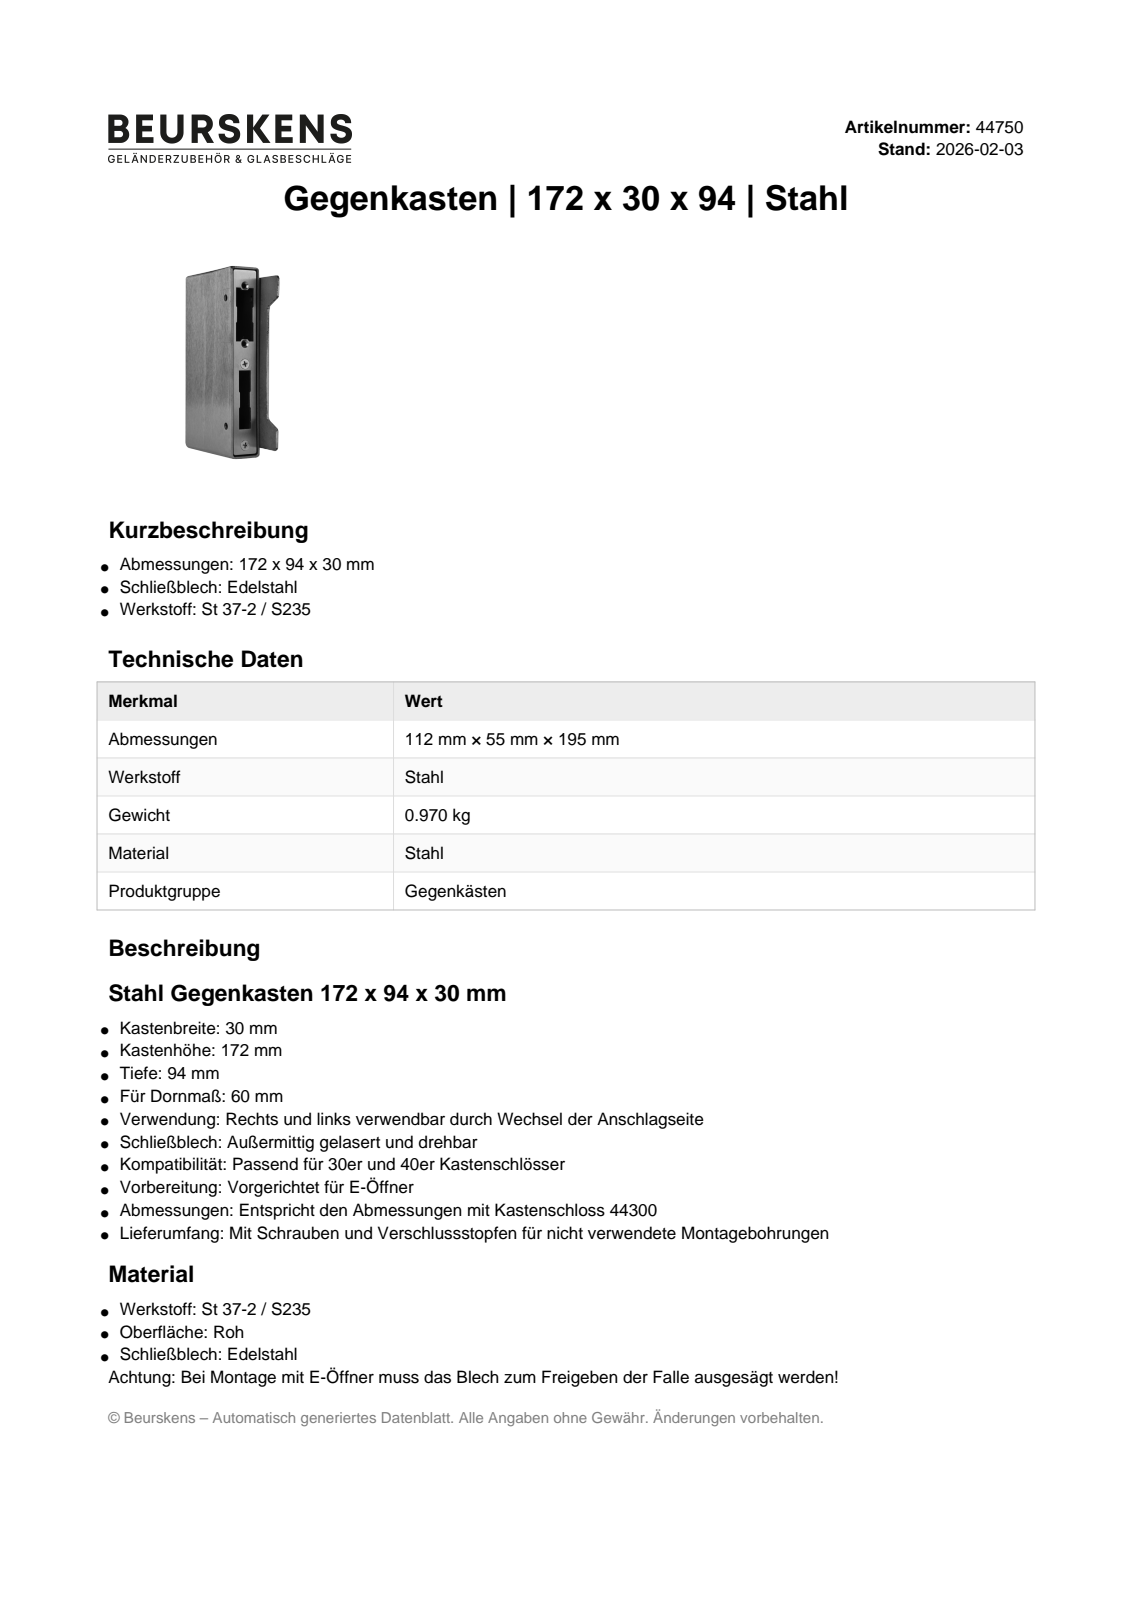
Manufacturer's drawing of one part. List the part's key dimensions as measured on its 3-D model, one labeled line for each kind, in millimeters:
Part name (STEP PRODUCT): 44750-1; 41540; 41525; 40941 (+2 more)
STEP written by: Autodesk Inventor 2023 (AUTOMOTIVE_DESIGN)
Units: millimetres
Bodies: 7 solids, 200 faces (136 planar, 38 cylindrical, 26 other)
Overall size (bounding box): 172 × 119 × 33.01
Volume: 127 318 mm³ · Surface area: 103 435 mm²
Round holes (diameter × count): ⌀4.2 ×2, ⌀4.3 ×2, ⌀4.5 ×2, ⌀5.5 ×2, ⌀6 ×2
Round bosses / shafts (diameter × count): ⌀5 ×4, ⌀9.3 ×2
Partial cylindrical surfaces — rounded edges, fillets, slot ends (radius × count): R4 ×8, R5 ×8, R2 ×4
Main face-to-face distances: 2.5, 27.5, 25, 30, 3, 5.5, 30.5, 33, 169.5, 91.5
Hole centre spacings: 18.25, 52, 70.25, 72.75, 91, 115, 143
